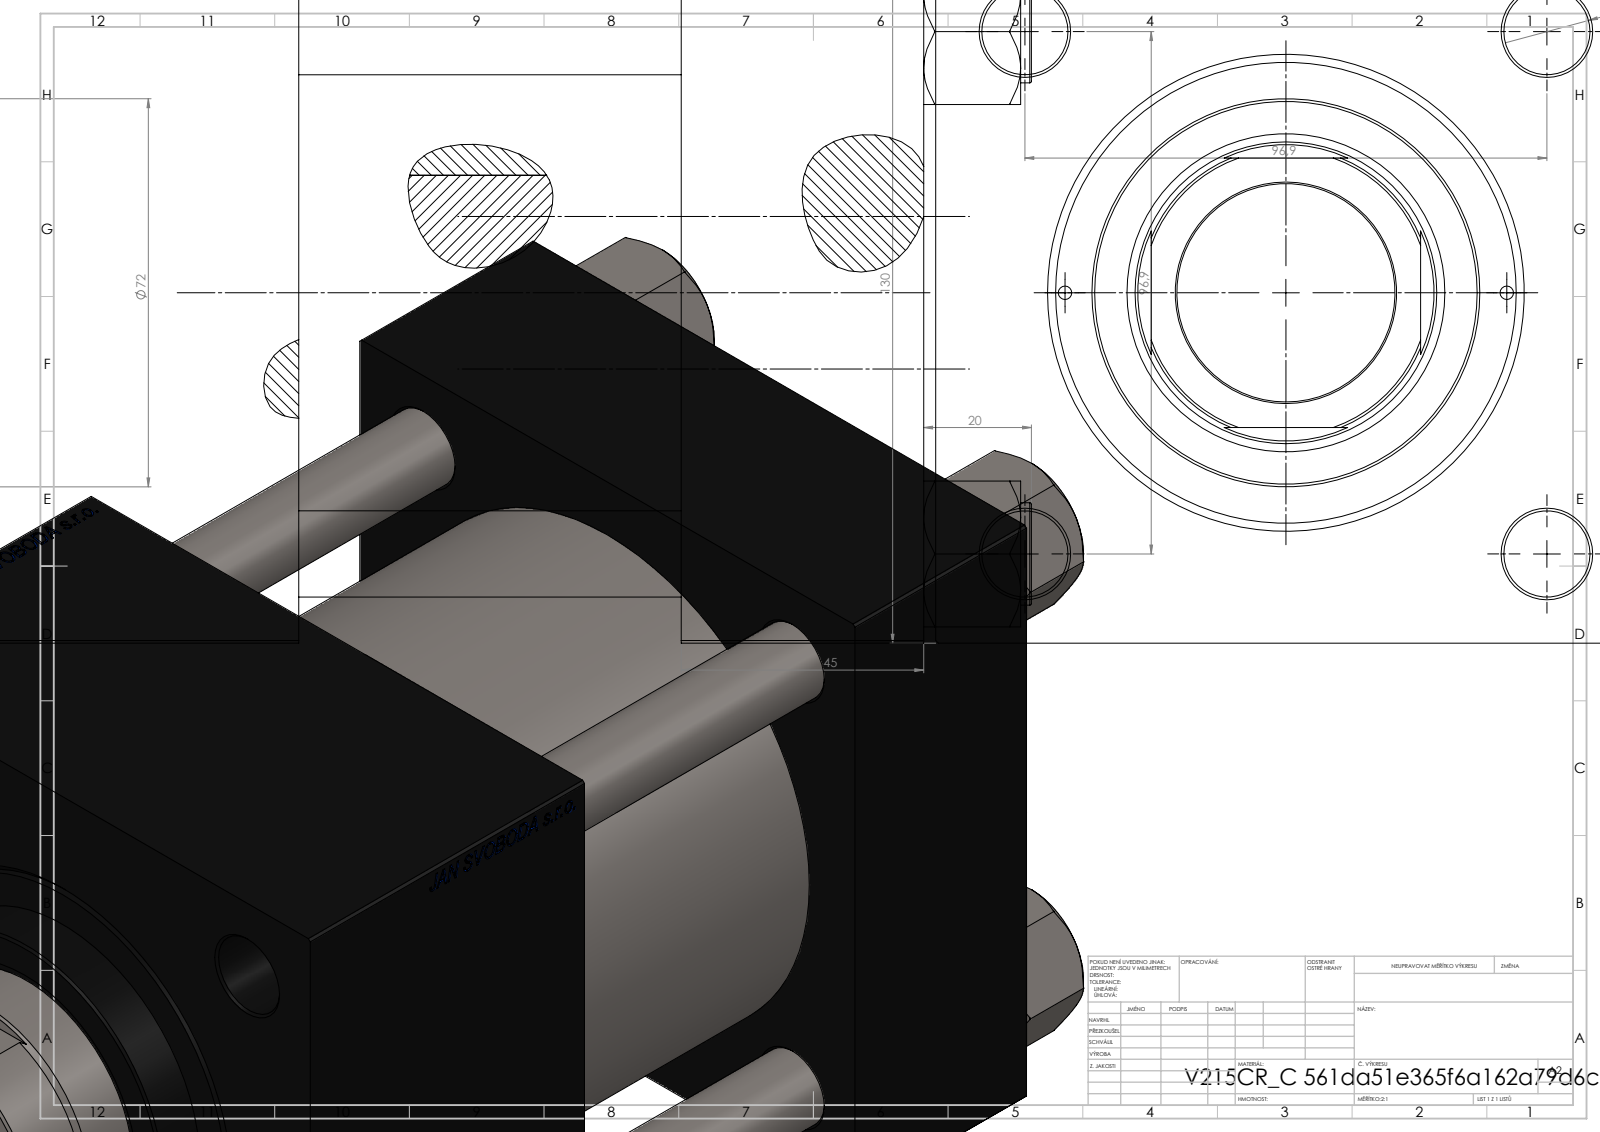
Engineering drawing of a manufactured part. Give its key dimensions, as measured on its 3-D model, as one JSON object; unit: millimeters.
{"part_name": "V215_VC_A; NUT_M5_C; V215CR_VCP_C; V215CR_C_TYCINKA (+1 more)", "step_written_by": "SolidWorks 2019 (CONFIG_CONTROL_DESIGN)", "units": "millimeters", "bodies": {"solids": 11, "faces": 1202, "planar": 576, "cylindrical": 90, "other": 536}, "overall_size": [243, 130, 130], "volume_mm3": 2475000, "surface_area_mm2": 333449, "round_holes": [[16, 4], [2.5, 2], [7, 2], [26.44, 2], [35, 2], [40.5, 1], [56, 1], [59, 1], [76, 1], [85.5, 1], [100, 1]], "round_bosses_or_shafts": [[19, 4], [106, 1], [72, 1]], "partial_cylinders_radius": [[27, 1]], "face_to_face_distances": [130, 45, 188, 143, 116, 71, 72, 20, 51, 96], "hole_center_spacings": [49.02, 68.52, 96.9, 101.73, 41, 137.04, 82, 118.5]}
